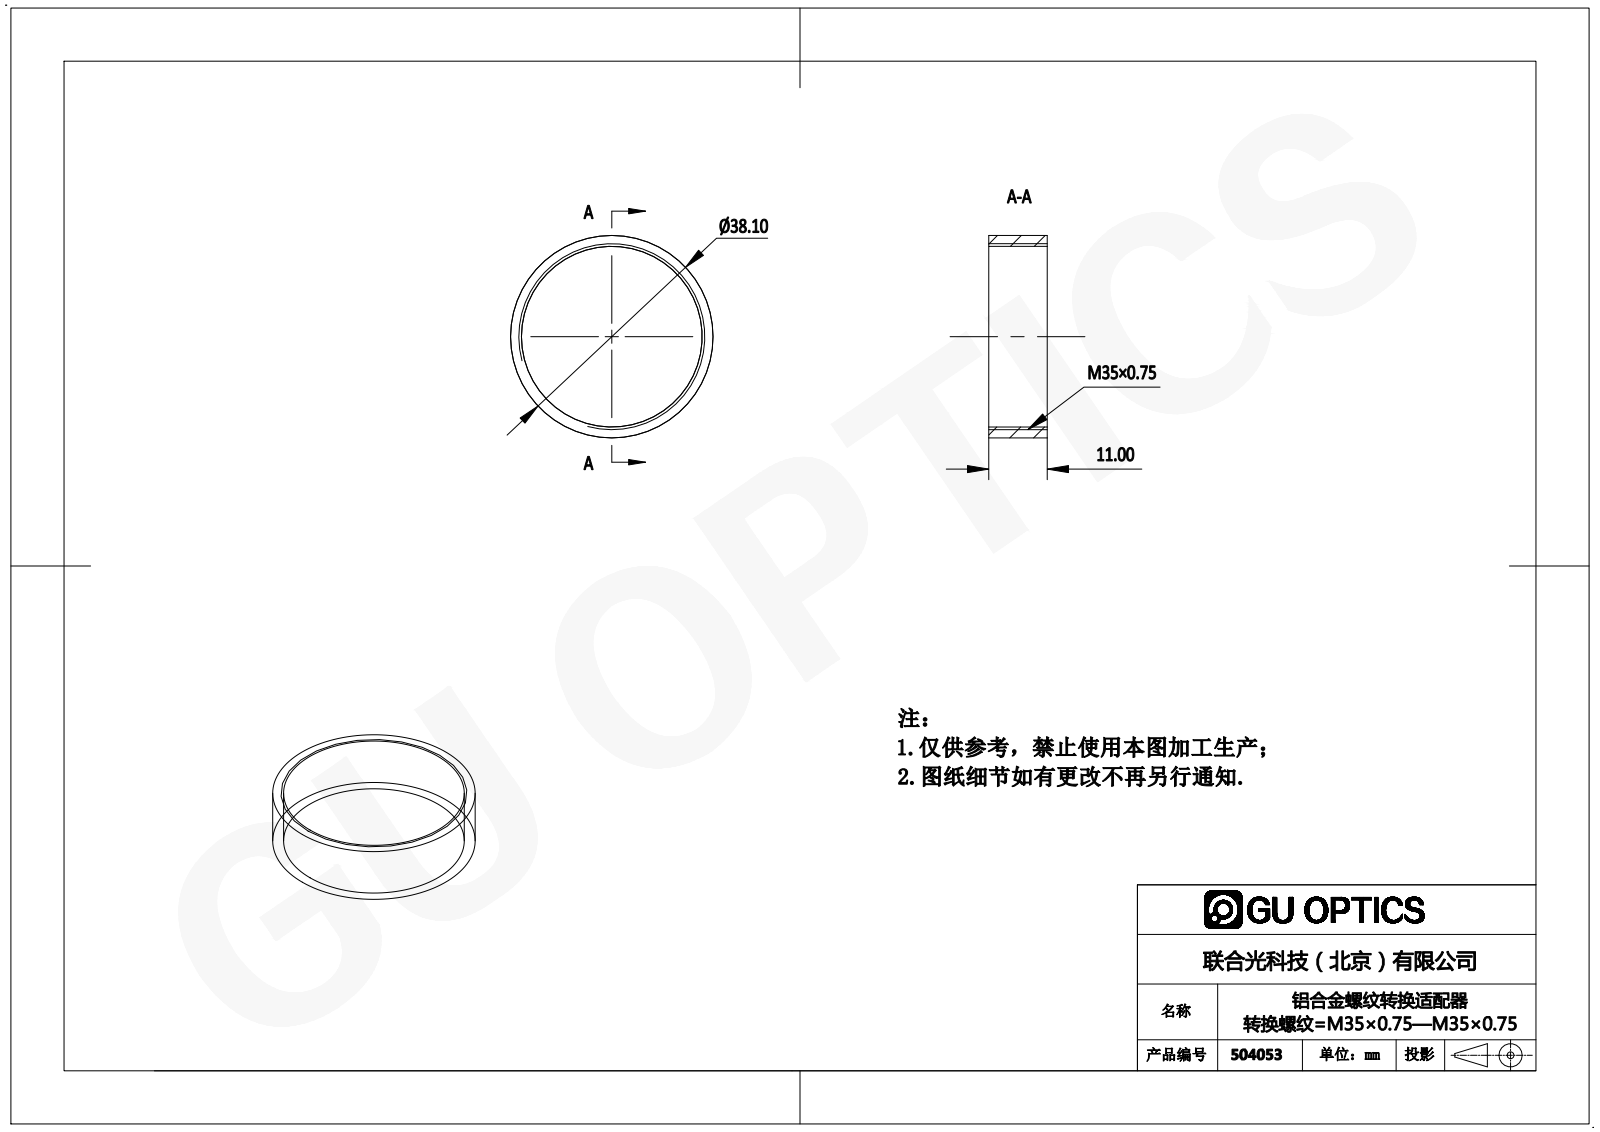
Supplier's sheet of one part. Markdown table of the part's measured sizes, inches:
| quantity | value |
| --- | --- |
| part name | 504053 |
| STEP written by | SolidWorks 2016 (AUTOMOTIVE_DESIGN) |
| units | inches |
| bodies | 1 solid, 6 faces (2 planar, 4 cylindrical, 0 other) |
| overall size | 1.5 × 1.5 × 0.433 |
| volume | 0.156 in³ |
| surface area | 4.582 in² |
| round holes (diameter × count) | 1.339 × 1 |
| round bosses / shafts (diameter × count) | 1.5 × 1 |
| main face-to-face distances | 0.433 |
